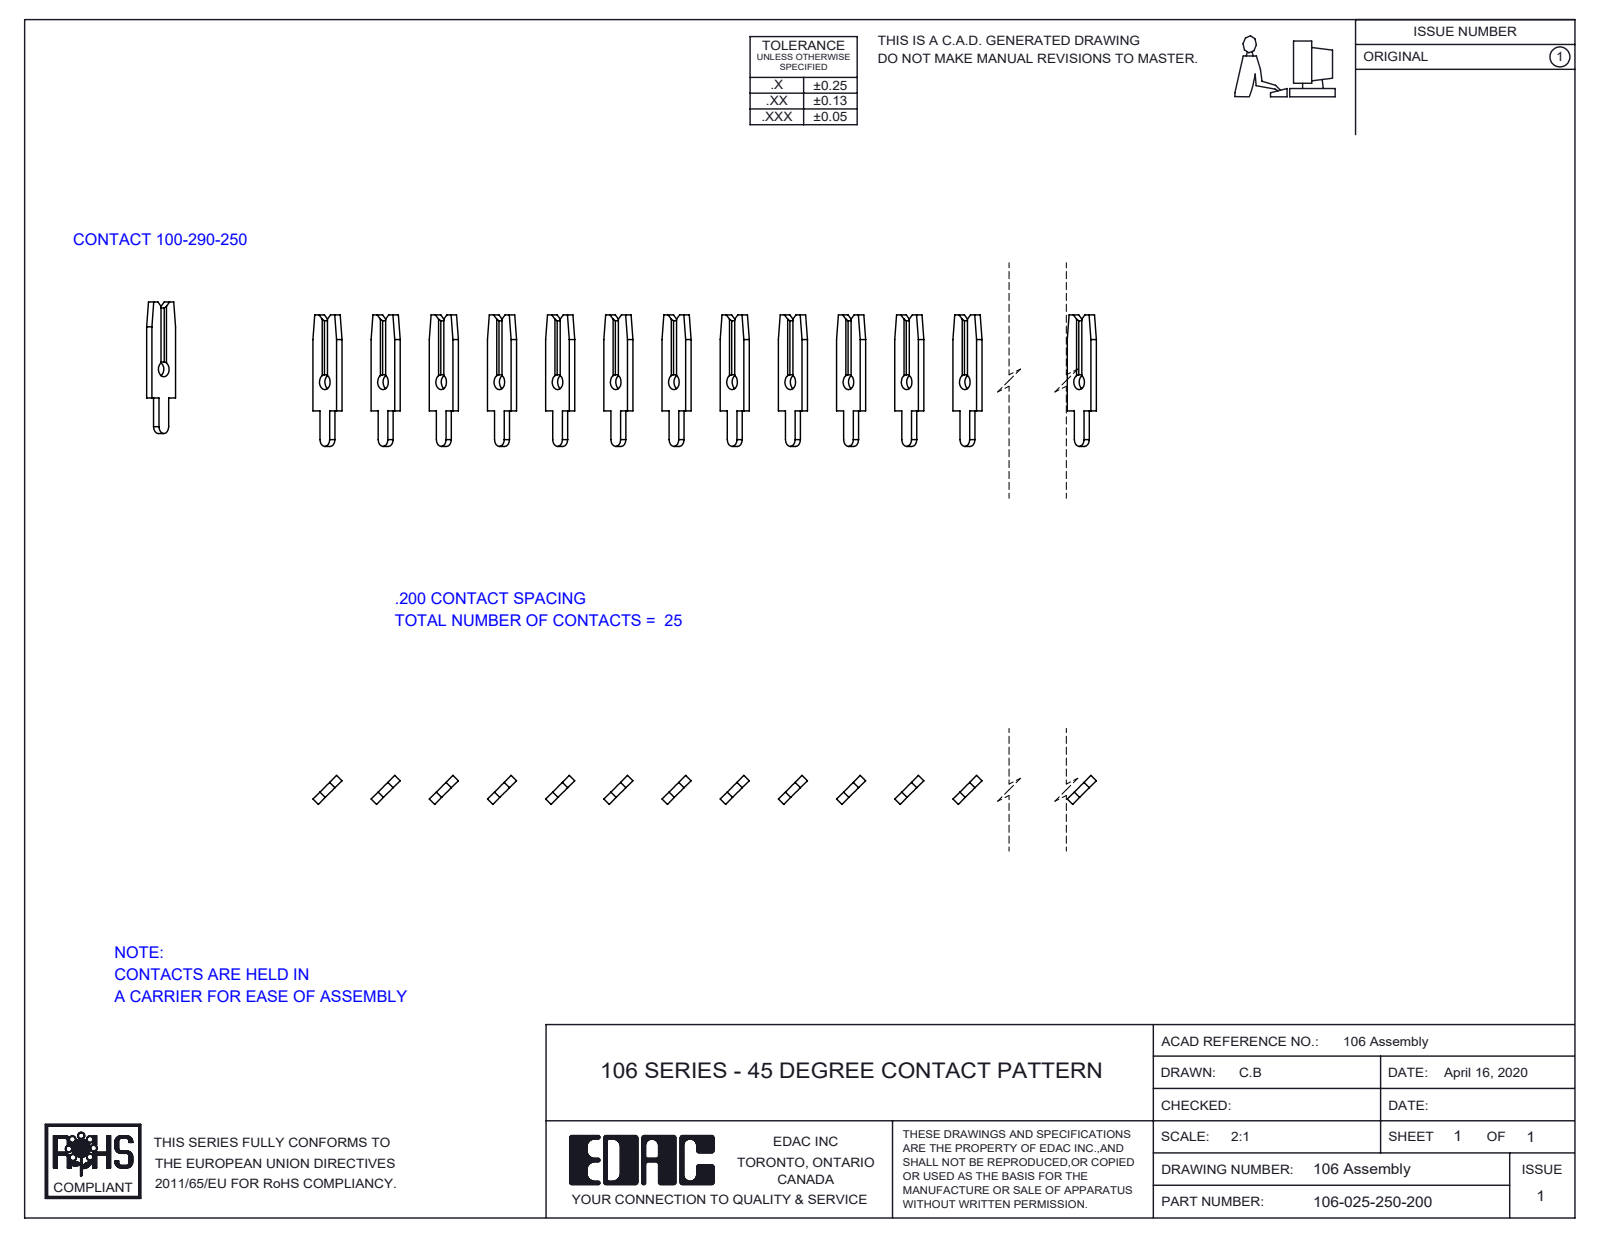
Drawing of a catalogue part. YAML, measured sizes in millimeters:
part_name: "106-025-250-200; 100-290-001_100-290-250"
step_written_by: "SolidWorks 2016 (CONFIG_CONTROL_DESIGN)"
units: millimeters
bodies: {solids: 25, faces: 600, planar: 500, cylindrical: 100, other: 0}
overall_size: [124.5, 11.5, 2.5]
volume: 390
surface_area: 1834
round_holes:
  - {diameter: 1.3, count: 25}
partial_cylinders:
  - {radius: 0.6, count: 25}
face_to_face_distances: [3.6, 21.5, 18, 7.2, 25.1, 14.4, 10.8, 28.7, 10.8, 39.5]
hole_center_spacings: [3.6, 7.2, 10.8, 28.7, 21.5, 43.1, 46.7, 25.1]
